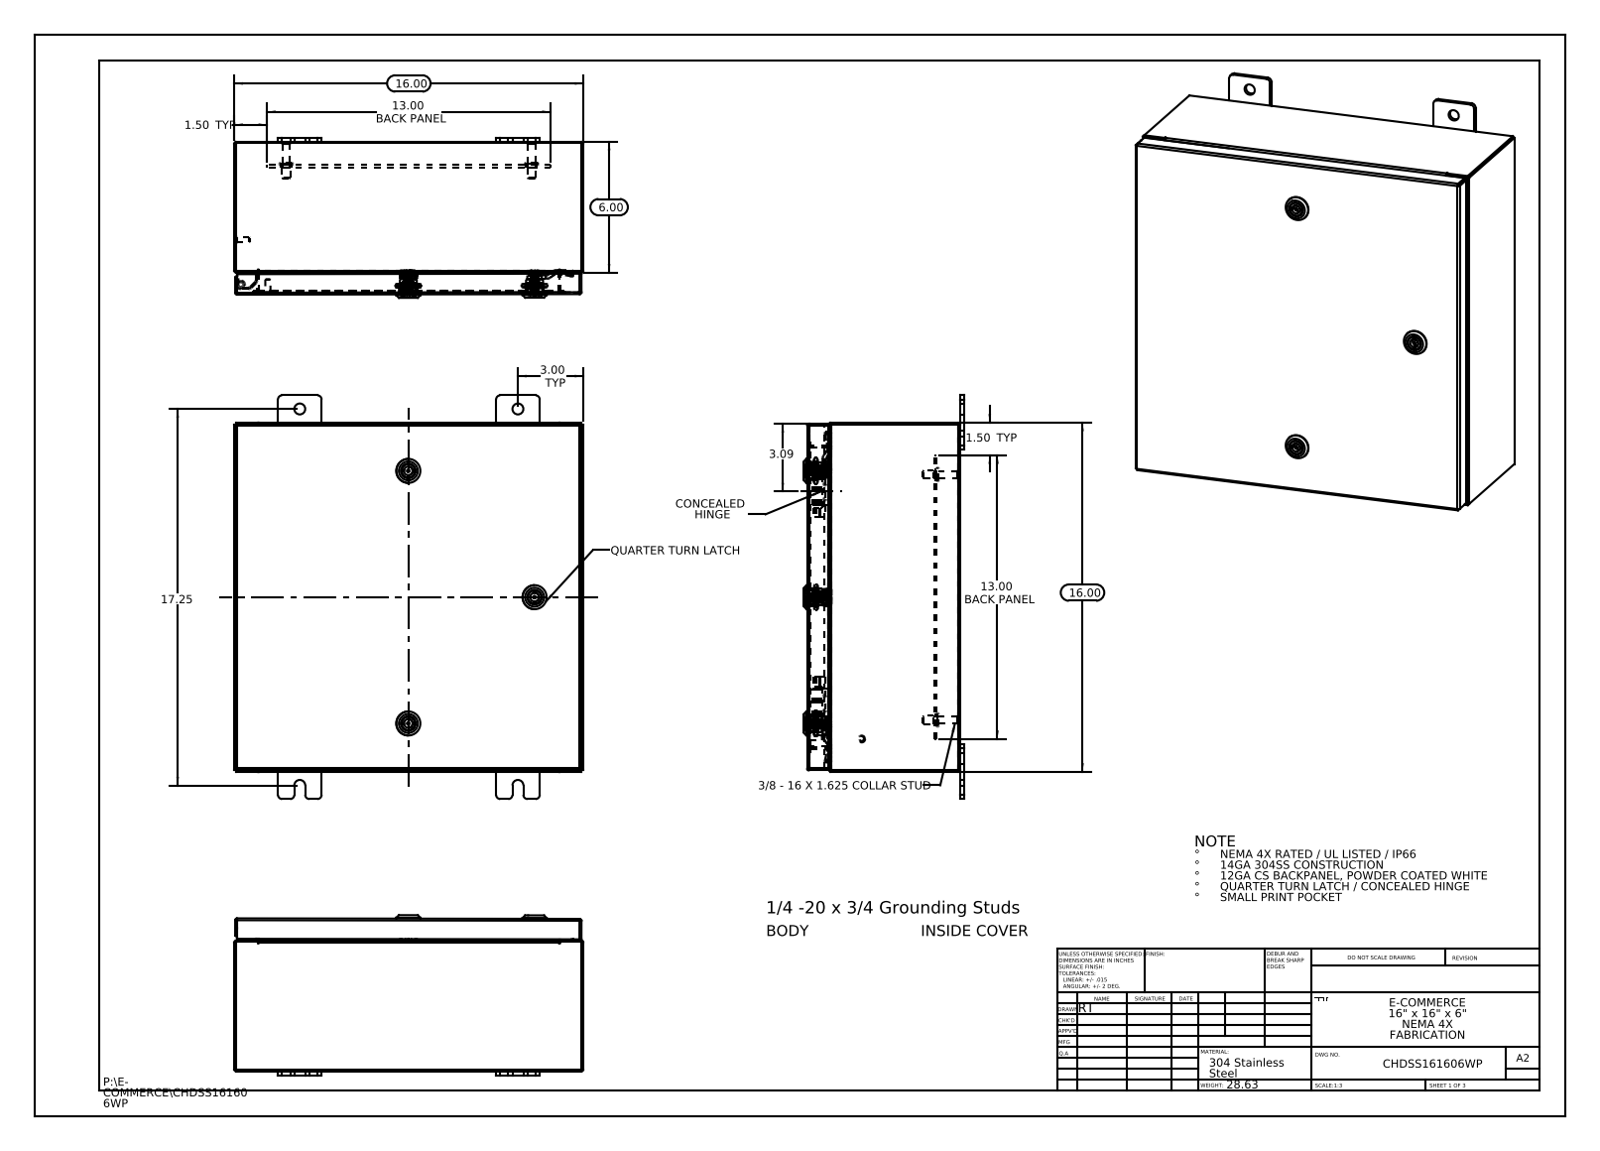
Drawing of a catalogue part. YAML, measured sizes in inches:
part_name: "Concealed Hinge Assembly; CHDSS161606WP Bottom; HW-CLH-E5-8004_Cam-232112-U-Industrilas; Concealed Hinge enclosure side (+8 more)"
step_written_by: "SolidWorks 2013 (CONFIG_CONTROL_DESIGN)"
units: inches
bodies: {solids: 37, faces: 2966, planar: 938, cylindrical: 930, other: 1098}
overall_size: [18.5, 16, 7.345]
volume: 102.6
surface_area: 2580
round_holes:
  - {diameter: 0.5, count: 8}
  - {diameter: 0.394, count: 6}
  - {diameter: 0.136, count: 4}
  - {diameter: 0.197, count: 3}
  - {diameter: 0.4, count: 3}
  - {diameter: 0.63, count: 3}
  - {diameter: 0.787, count: 3}
  - {diameter: 0.211, count: 2}
round_bosses_or_shafts:
  - {diameter: 0.236, count: 5}
  - {diameter: 0.625, count: 4}
  - {diameter: 0.375, count: 4}
  - {diameter: 0.33, count: 4}
  - {diameter: 1.102, count: 3}
  - {diameter: 0.78, count: 3}
  - {diameter: 0.626, count: 3}
  - {diameter: 0.61, count: 3}
partial_cylinders:
  - {radius: 0.006, count: 99}
  - {radius: 0.118, count: 99}
  - {radius: 0.028, count: 36}
  - {radius: 0.19, count: 24}
  - {radius: 0.013, count: 18}
  - {radius: 0.088, count: 18}
  - {radius: 0.02, count: 12}
  - {radius: 0.197, count: 12}
face_to_face_distances: [0.075, 15.925, 15.85, 16, 1, 1.075, 1.179, 1.104, 0.104, 5.925]
hole_center_spacings: [11.576, 8.185, 8.184, 1.858, 3.065, 8.185, 8.186, 8.186]
